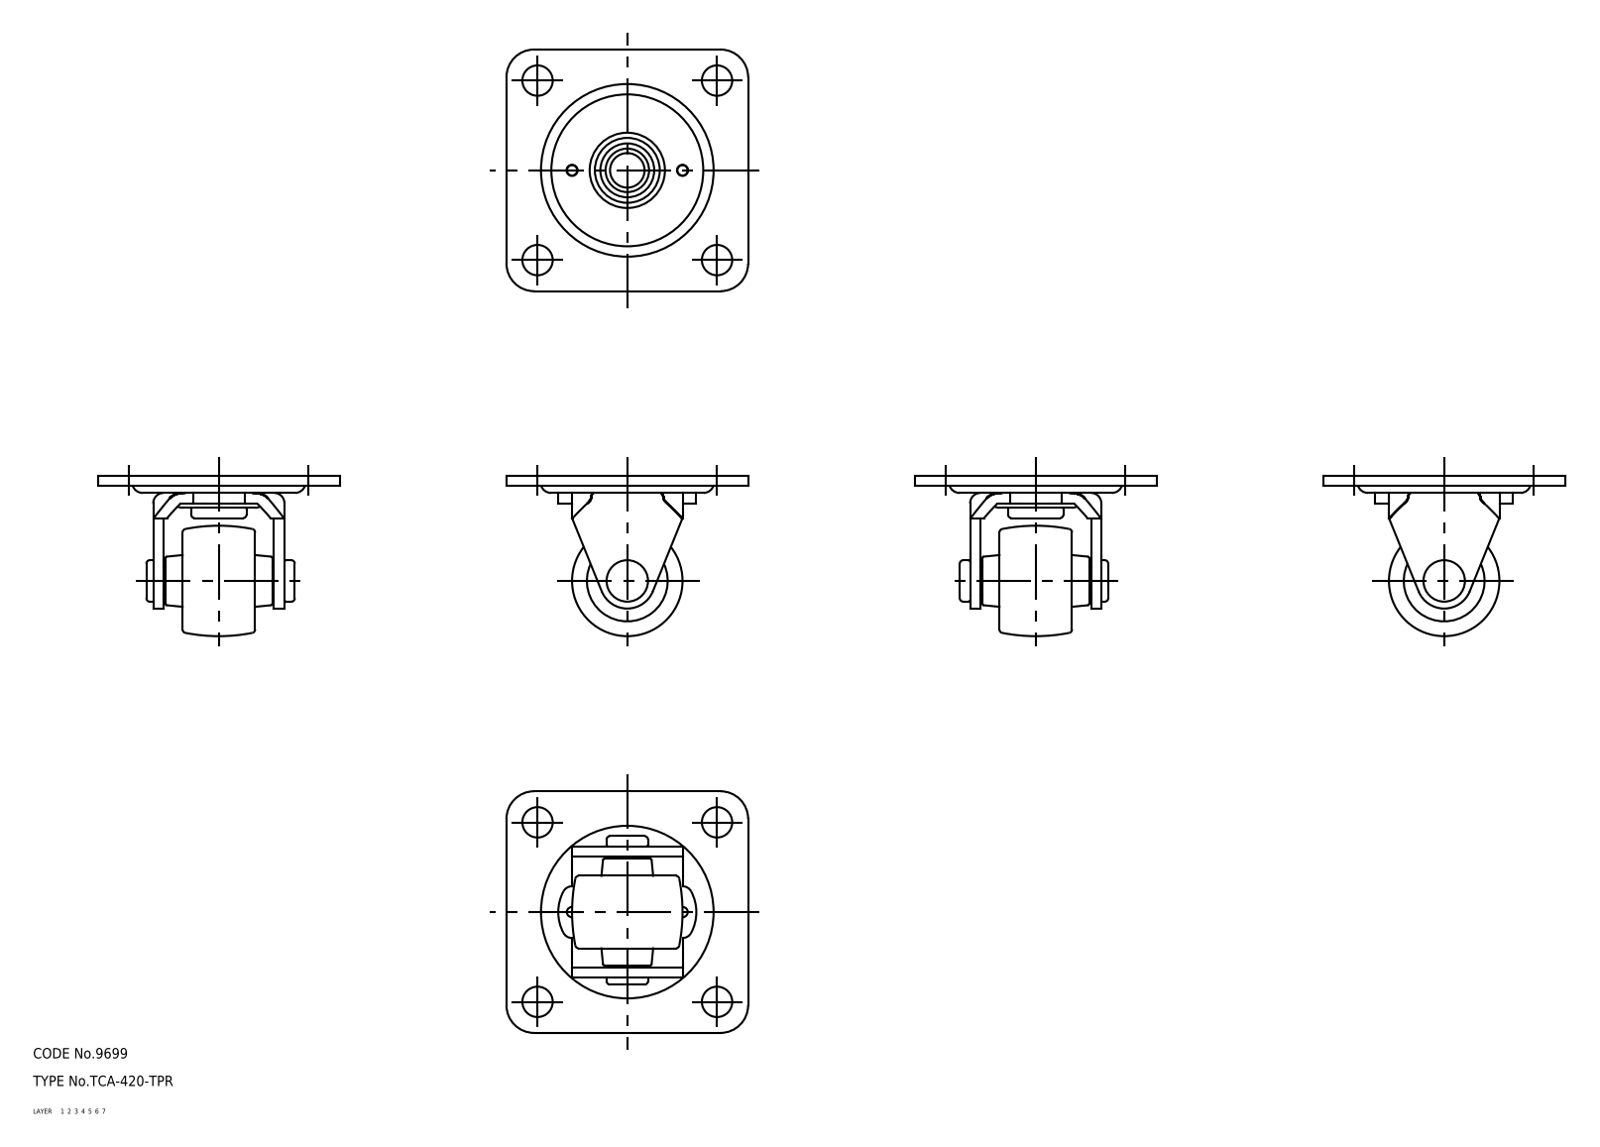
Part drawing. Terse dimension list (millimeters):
name: wheel; mounting plate; main shaft; axle (+1 more)
written by: CADfix (AUTOMOTIVE_DESIGN)
unit: mm
bodies: 5 solids, 179 faces (0 planar, 0 cylindrical, 179 other)
size: 70 × 70 × 46.5
volume: 39 113 mm³; area: 23 701 mm²
